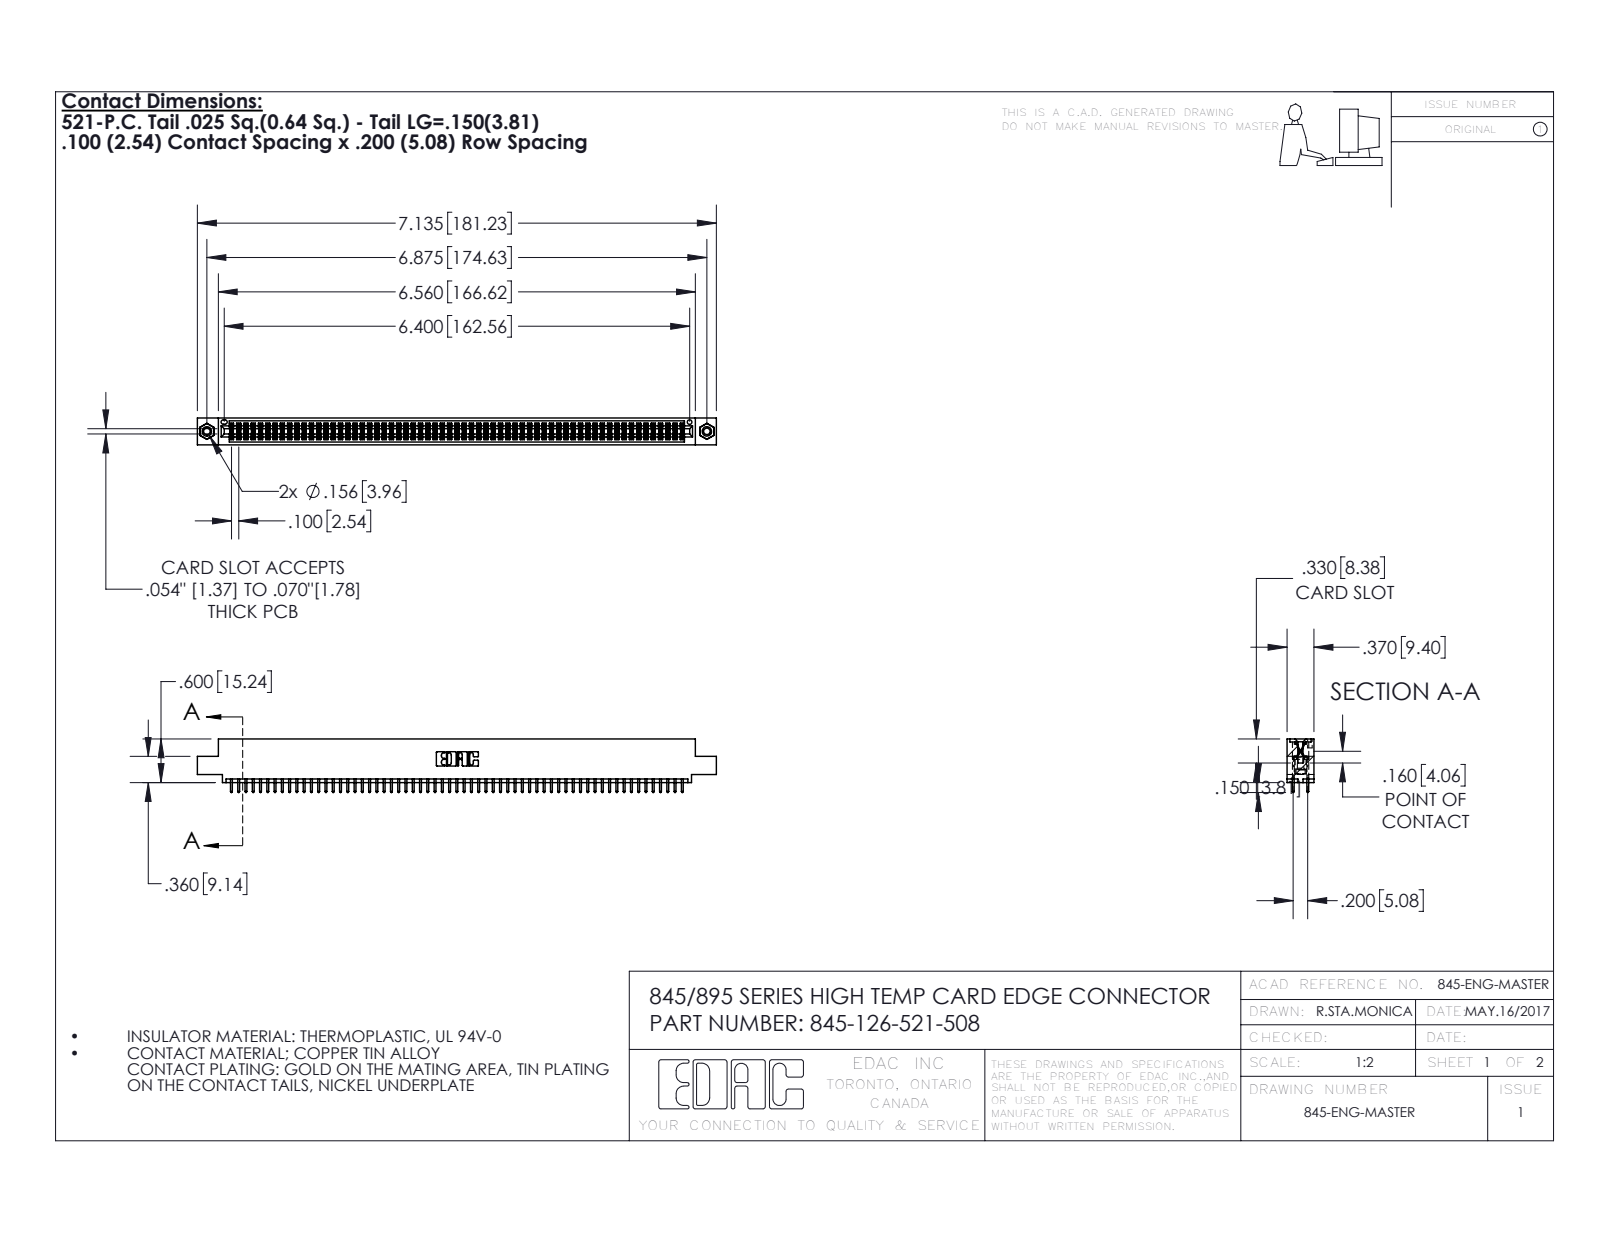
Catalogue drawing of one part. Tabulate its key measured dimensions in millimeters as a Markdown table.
| quantity | value |
| --- | --- |
| part name | 345-250-001_345-250-003-102; 345 Part_0.110 Offset - 0.156 Dia-TI; 345-292-001_345-293-121; 345-126-521-508 |
| STEP written by | SolidWorks 2016 (CONFIG_CONTROL_DESIGN) |
| units | millimeters |
| bodies | 129 solids, 6490 faces (4274 planar, 2200 cylindrical, 16 other) |
| overall size | 181.2 × 18.7 × 9.4 |
| volume | 17 670 mm³ |
| surface area | 26 300 mm² |
| round holes (diameter × count) | 2.3 × 2, 3.2 × 2, 4 × 2, 1.6 × 1 |
| round bosses / shafts (diameter × count) | 3.9 × 2 |
| partial cylindrical surfaces (radius × count) | 0.2 × 189, 0.3 × 126, 0.3 × 22, 0.2 × 6, 0.8 × 6, 0.7 × 3, 0.4 × 2, 0.5 × 2 |
| main face-to-face distances | 1.8, 7.6, 5.1, 2.5, 6.9, 0.6, 9.4, 5.7, 4.4, 3.8 |
| hole center spacings | 6.9, 168.6, 174.6 |
